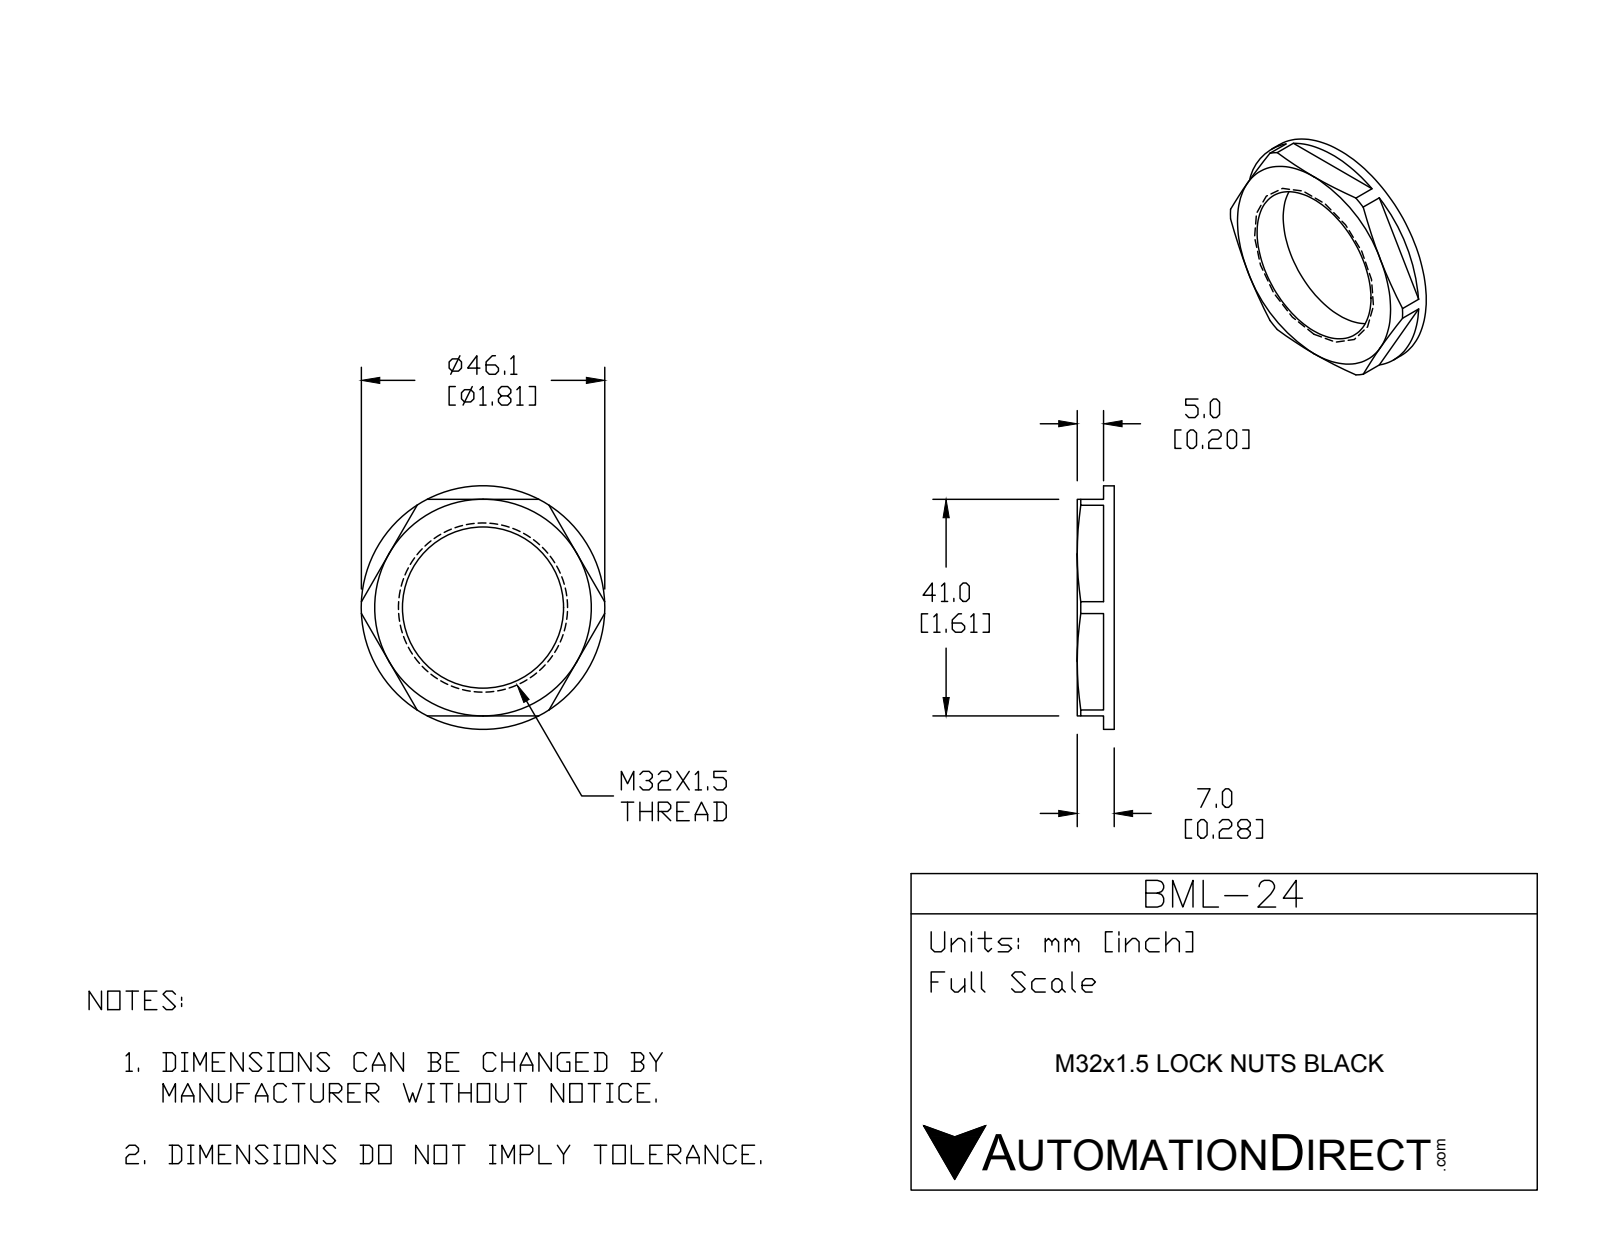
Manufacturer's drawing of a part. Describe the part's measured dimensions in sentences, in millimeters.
The part is named "BML-24". Its 3-D file was written by "SolidWorks 2015 (CONFIG_CONTROL_DESIGN)". It is 1 solid with 33 faces: 17 planar, 10 cylindrical and 6 other. Overall it measures 46.1 by 46.1 by 7 millimeters. Its volume is 5 449 cubic millimeters and its surface area 3 507 square millimeters. Round holes: 3 of diameter 1.5, 1 of diameter 30.5. Round bosses or shafts: 1 of diameter 46.1. The main face-to-face distances are 7, 41, 2, 5, 1.7, 6.7. The hole center spacings are 21.6, 37.41, 37.42.
